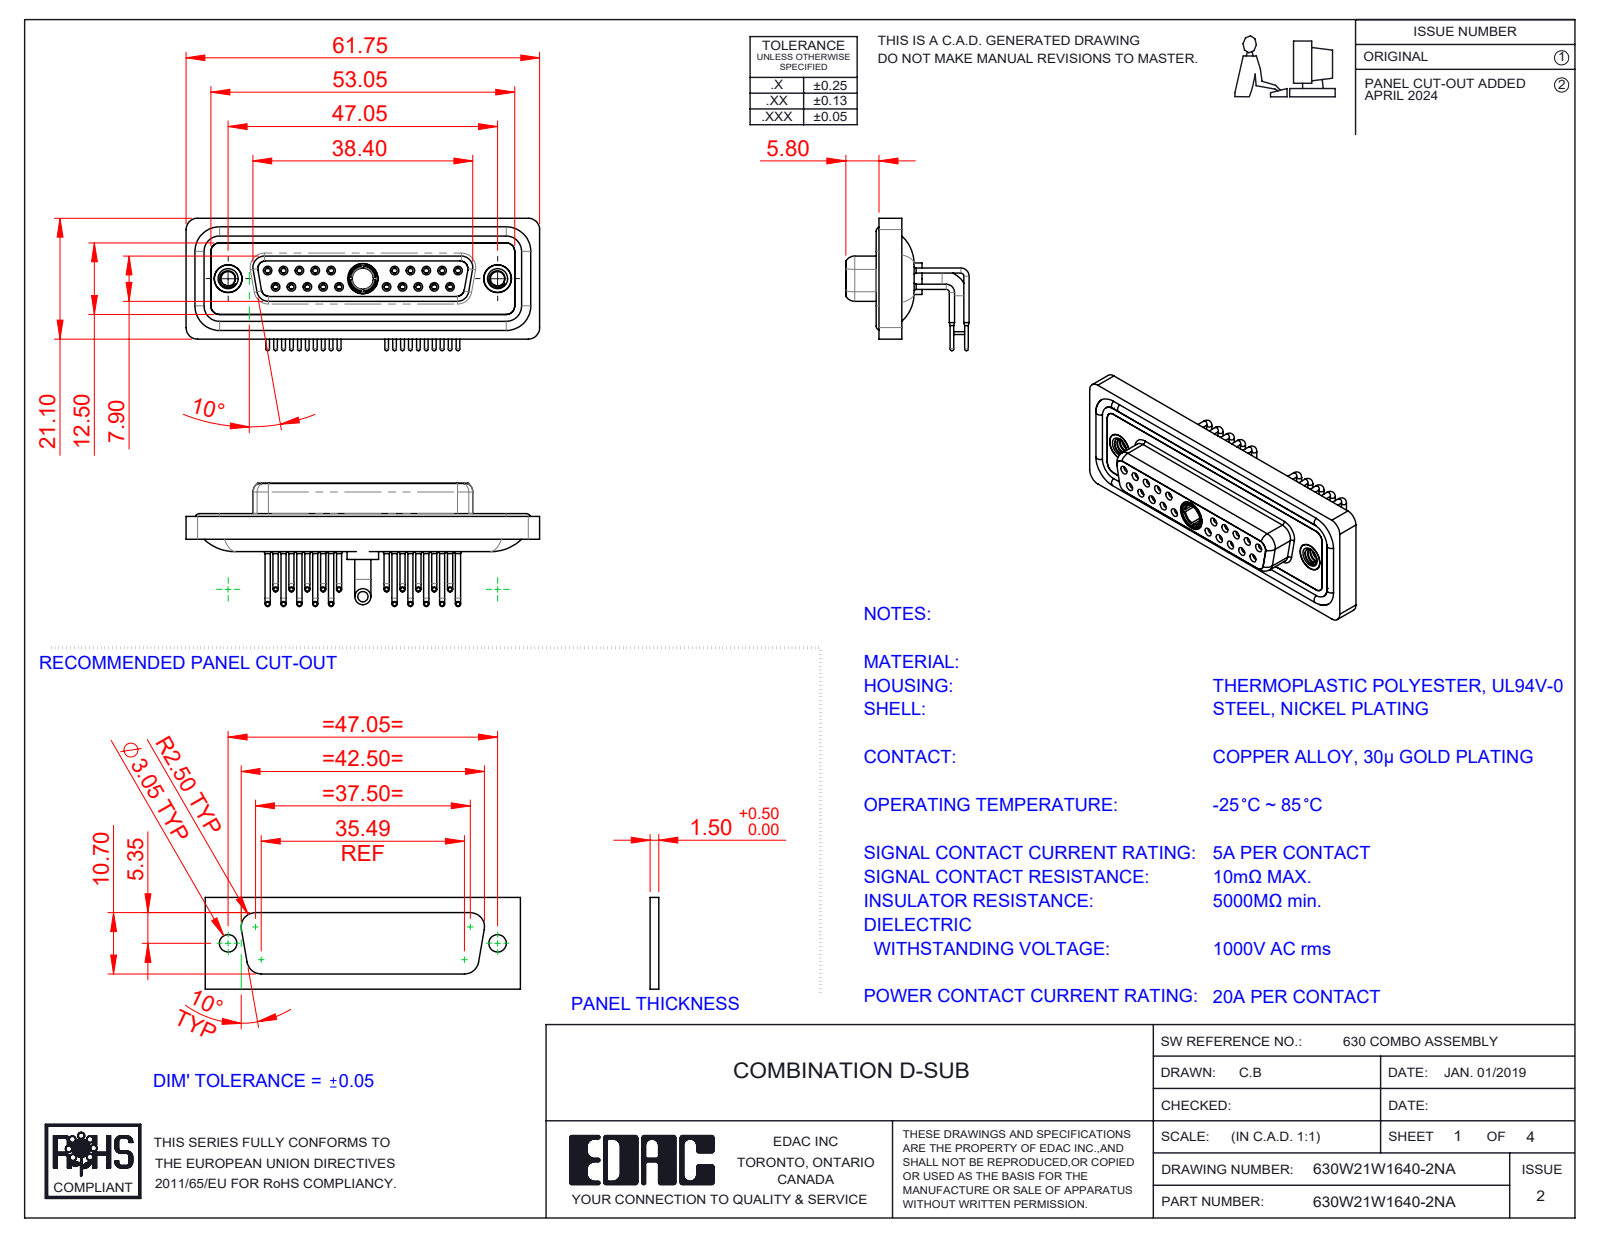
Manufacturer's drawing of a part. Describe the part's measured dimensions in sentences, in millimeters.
The part is named "630Combo Threaded Rivet_A; 630Combo Contact Row 2_50 Contacts; 630Combo Housing_21W1; Power Socket_20A RA (+5 more)". Its 3-D file was written by "SolidWorks 2023 (CONFIG_CONTROL_DESIGN)". It is 29 solids with 1518 faces: 434 planar, 671 cylindrical and 413 other. Overall it measures 61.75 by 23.12 by 21.53 millimeters. Its volume is 8 498 cubic millimeters and its surface area 14 783 square millimeters. Round holes: 20 of diameter 0.9, 20 of diameter 1.1, 20 of diameter 1.5, 20 of diameter 2, 10 of diameter 1.6, 10 of diameter 1.7, 3 of diameter 4.85, 2 of diameter 2.5, 2 of diameter 4, 2 of diameter 4.05, 2 of diameter 5, 1 of diameter 3.7. Round bosses or shafts: 20 of diameter 0.9, 20 of diameter 0.65, 14 of diameter 1.6, 2 of diameter 4.95, 2 of diameter 4.8, 2 of diameter 2.8, 1 of diameter 5.5, 1 of diameter 5.2. Partial cylindrical surfaces (rounded edges, fillets, slot ends): 18 of radius 1.5, 18 of radius 2, 8 of radius 1.35, 8 of radius 1.6, 4 of radius 0.25, 4 of radius 0.5, 4 of radius 0.6, 4 of radius 0.65. The main face-to-face distances are 0.4, 1.8, 4.1, 1.6, 1.1, 2.5, 3.1, 1.5, 9.8, 0.45. The hole center spacings are 3.16, 2.77, 5.54, 8.31, 5.04, 19.39, 20.97, 22.16.
